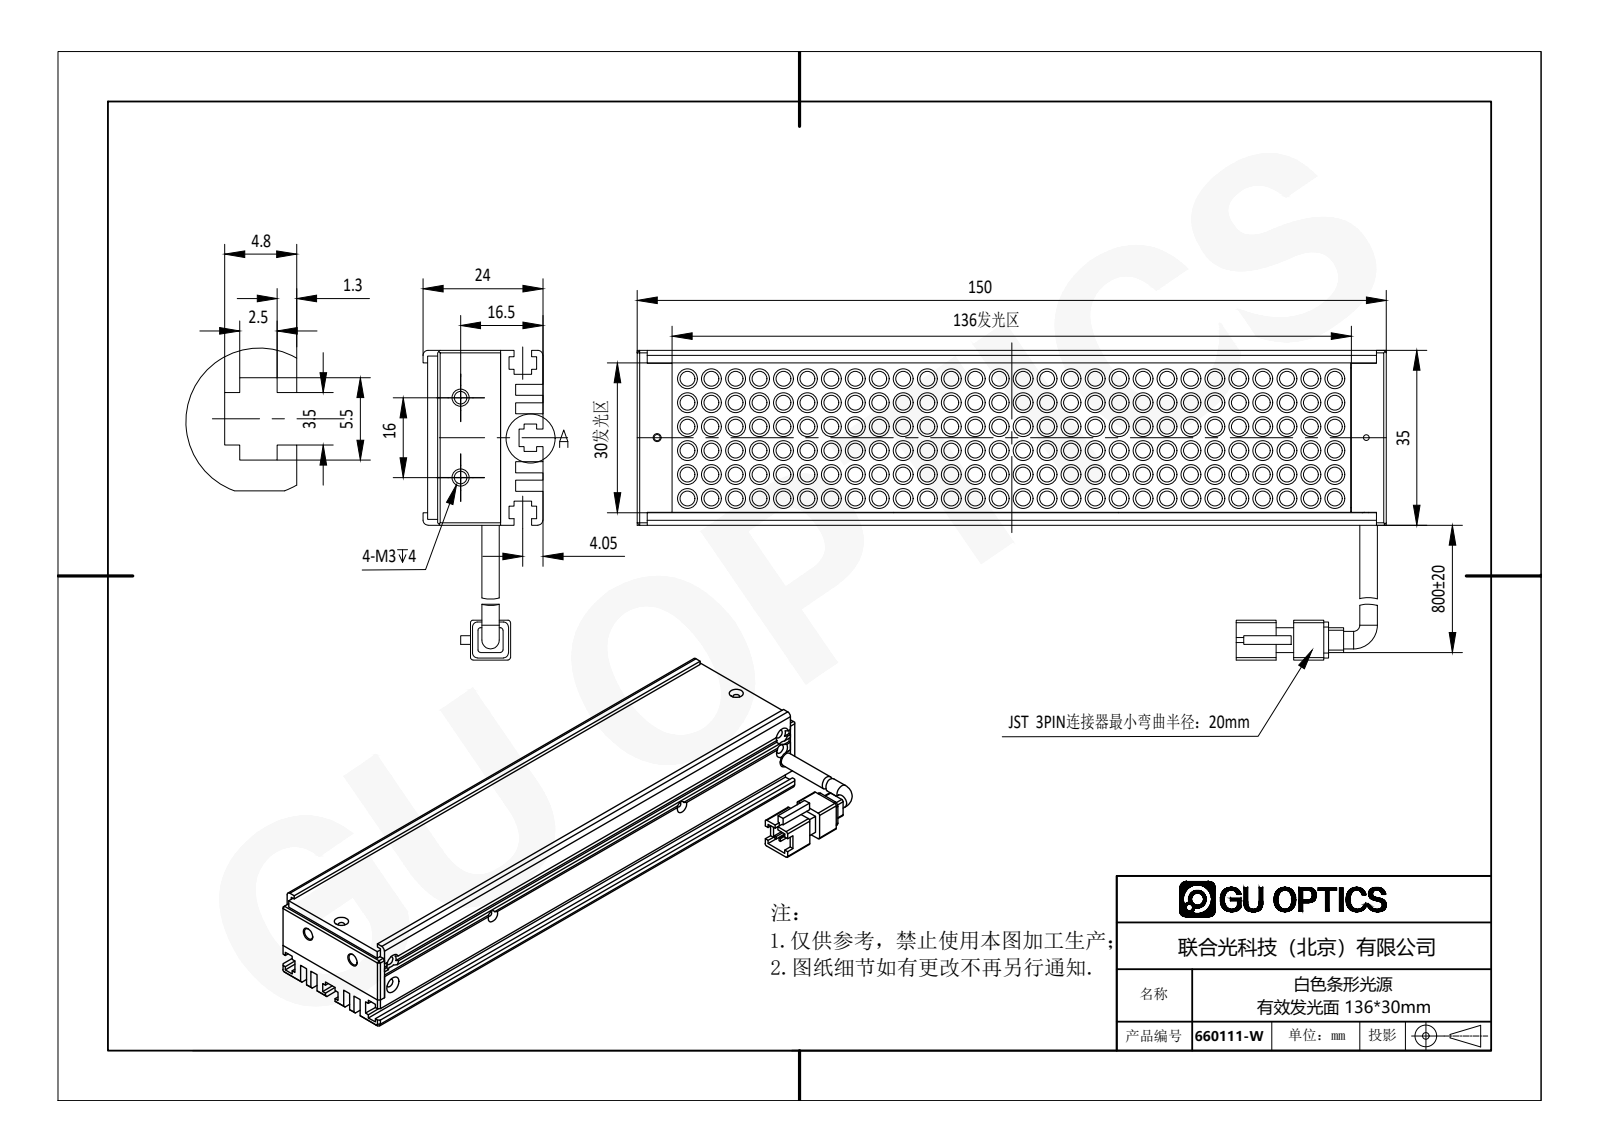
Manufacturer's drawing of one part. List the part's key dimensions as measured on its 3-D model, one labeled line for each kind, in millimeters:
Part name (STEP PRODUCT): 660111-W
STEP written by: SolidWorks 2016 (AUTOMOTIVE_DESIGN)
Units: millimetres
Bodies: 8 solids, 1543 faces (480 planar, 765 cylindrical, 298 other)
Overall size (bounding box): 150 × 62 × 24
Volume: 66 196 mm³ · Surface area: 68 375 mm²
Round holes (diameter × count): ⌀1.6 ×5, ⌀1.25 ×4, ⌀2.2 ×4, ⌀1.7 ×2, ⌀2.5 ×2, ⌀3 ×2, ⌀2.4 ×1
Round bosses / shafts (diameter × count): ⌀4 ×168, ⌀3 ×168, ⌀3.5 ×2
Partial cylindrical surfaces — rounded edges, fillets, slot ends (radius × count): R1 ×12, R0.5 ×8, R1.65 ×1
Main face-to-face distances: 12, 8.5, 2, 3.5, 10.5, 14, 1, 2.5, 3.7, 15.5
Hole centre spacings: 7, 36.17, 104.06, 140, 2.5, 4.5, 16, 36
